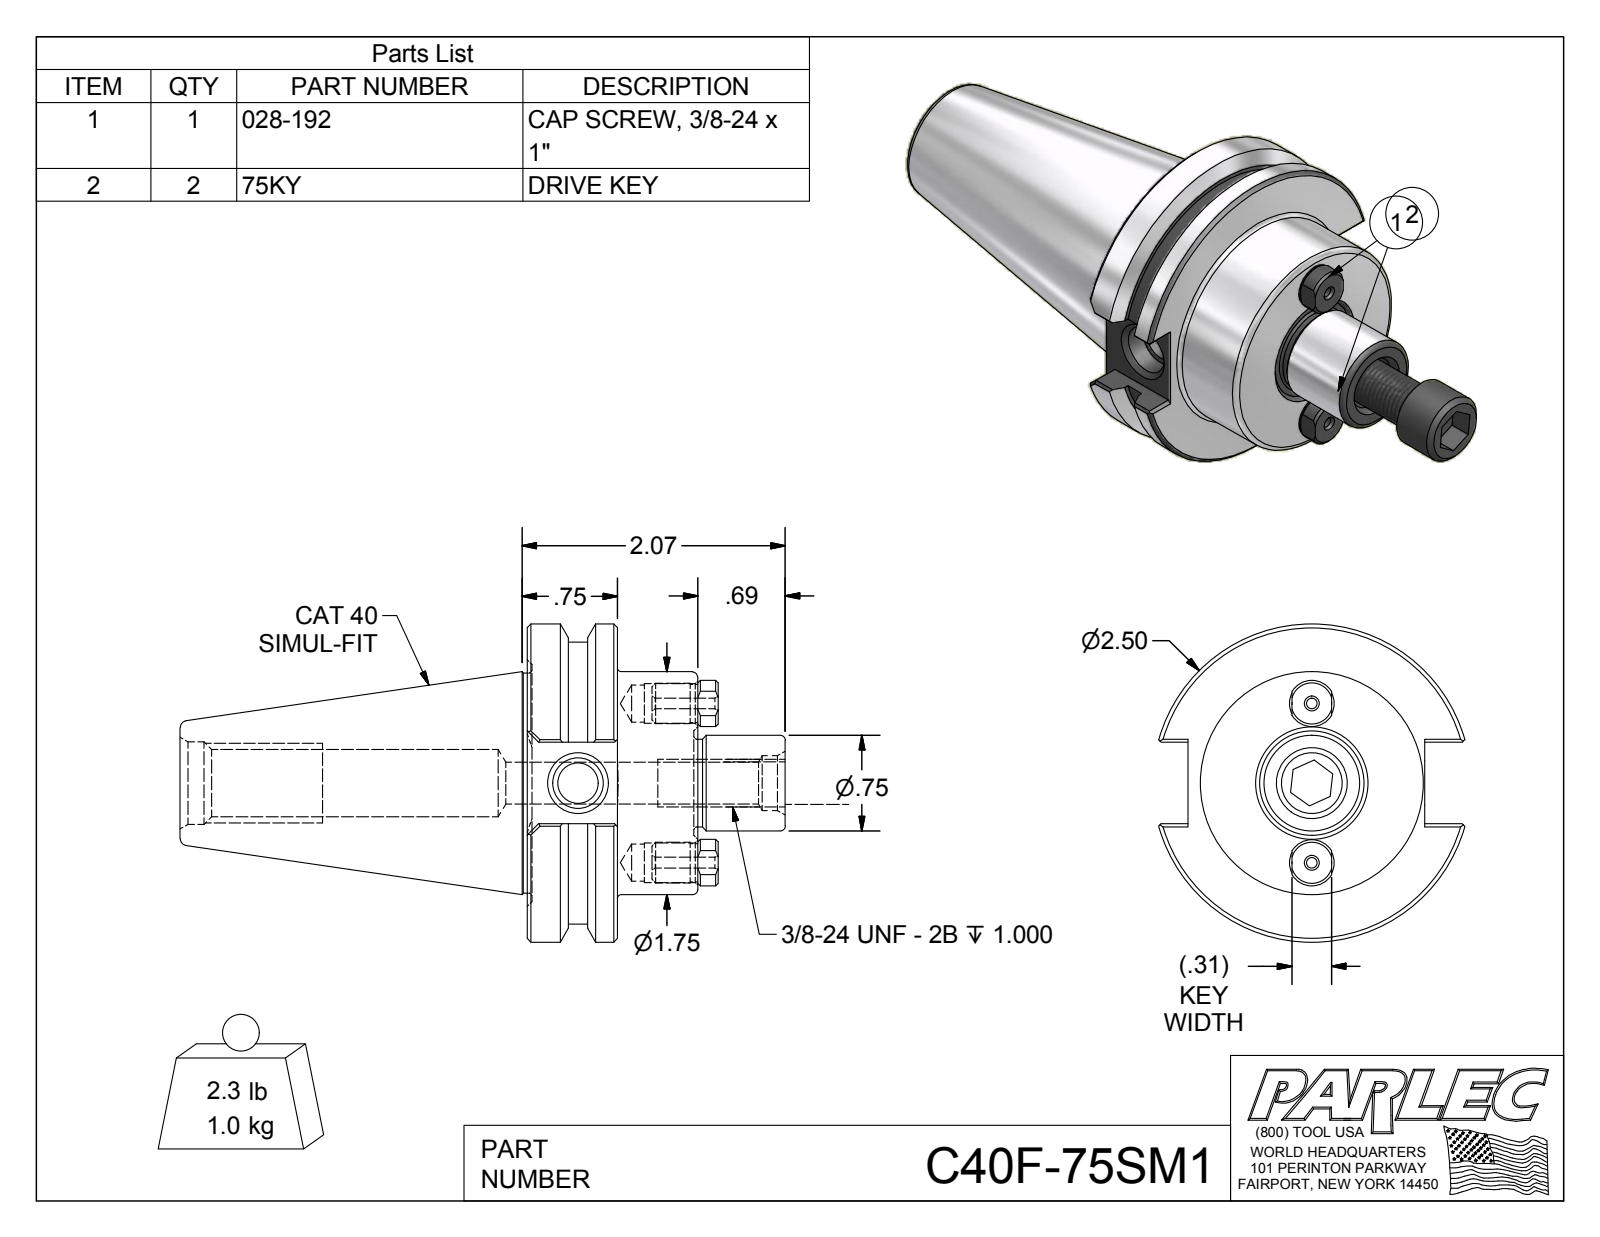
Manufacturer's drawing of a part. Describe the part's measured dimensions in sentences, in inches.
The part is named "C40F-75SM1; C40F-75SM1-1; 75KY; 028-192". Its 3-D file was written by "Autodesk Inventor 2012 (AUTOMOTIVE_DESIGN)". It is 4 solids with 140 faces: 58 planar, 32 cylindrical and 50 other. Overall it measures 5.626 by 2.5 by 2.406 inches. Its volume is 8.269 cubic inches and its surface area 43.04 square inches. Round holes: 2 of diameter 0.084, 2 of diameter 0.292, 2 of diameter 0.312, 1 of diameter 0.315, 1 of diameter 0.33, 1 of diameter 0.399, 1 of diameter 0.43, 1 of diameter 0.527, 1 of diameter 0.648. Round bosses or shafts: 2 of diameter 0.318, 2 of diameter 0.3, 1 of diameter 2.5, 1 of diameter 2.215, 1 of diameter 1.75, 1 of diameter 1.73, 1 of diameter 0.75, 1 of diameter 0.69. Partial cylindrical surfaces (rounded edges, fillets, slot ends): 2 of radius 0.183. The main face-to-face distances are 0.63, 0.711, 1.341, 1.86, 0.64, 0.037, 0.674, 1.304, 0.5, 0.19. The hole center spacings are 0.625, 1.25.
